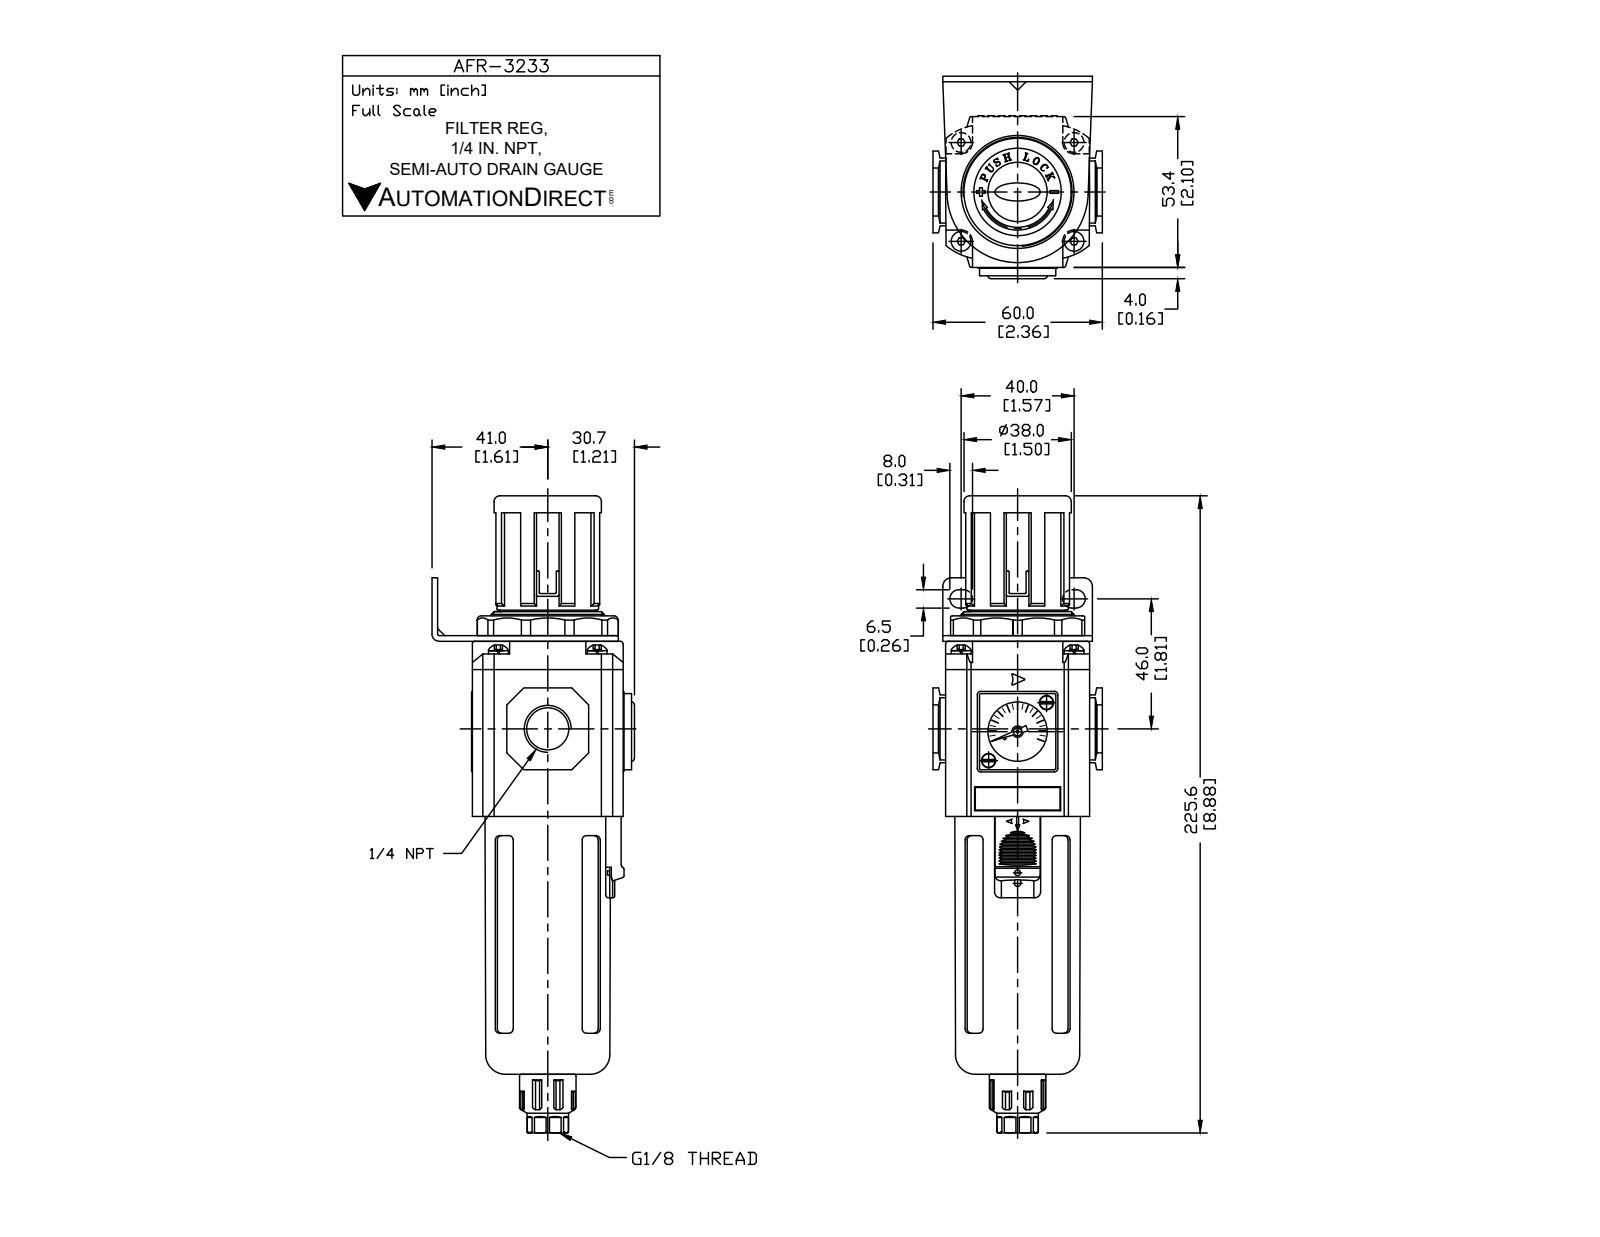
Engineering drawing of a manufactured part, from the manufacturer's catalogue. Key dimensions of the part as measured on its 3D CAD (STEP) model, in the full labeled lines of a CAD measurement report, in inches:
Part name (STEP PRODUCT): AFR-3233
STEP written by: SolidWorks 2015 (CONFIG_CONTROL_DESIGN)
Units: inches
Bodies: 16 solids, 606 faces (370 planar, 172 cylindrical, 64 other)
Overall size (bounding box): 8.882 × 2.835 × 2.362
Volume: 16.86 in³ · Surface area: 108.2 in²
Round holes (diameter × count): ⌀0.118 ×6, ⌀0.079 ×1, ⌀0.244 ×1, ⌀0.438 ×1, ⌀0.63 ×1, ⌀0.827 ×1, ⌀1.181 ×1, ⌀1.26 ×1, ⌀1.386 ×1
Round bosses / shafts (diameter × count): ⌀0.217 ×4, ⌀0.106 ×2, ⌀1.732 ×1, ⌀1.575 ×1, ⌀1.496 ×1, ⌀1.417 ×1, ⌀1.319 ×1, ⌀0.806 ×1
Partial cylindrical surfaces — rounded edges, fillets, slot ends (radius × count): R0.087 ×18, R0.039 ×12, R0.047 ×10, R0.02 ×8, R0.374 ×8, R0.128 ×6, R0.157 ×5, R0.012 ×4
Main face-to-face distances: 0.079, 2.441, 2.52, 2.102, 2.008, 1.559, 0.039, 2.185, 2.063, 0.177
Hole centre spacings: 1.046, 0.571, 1.378, 1.575, 2.093, 1.141
